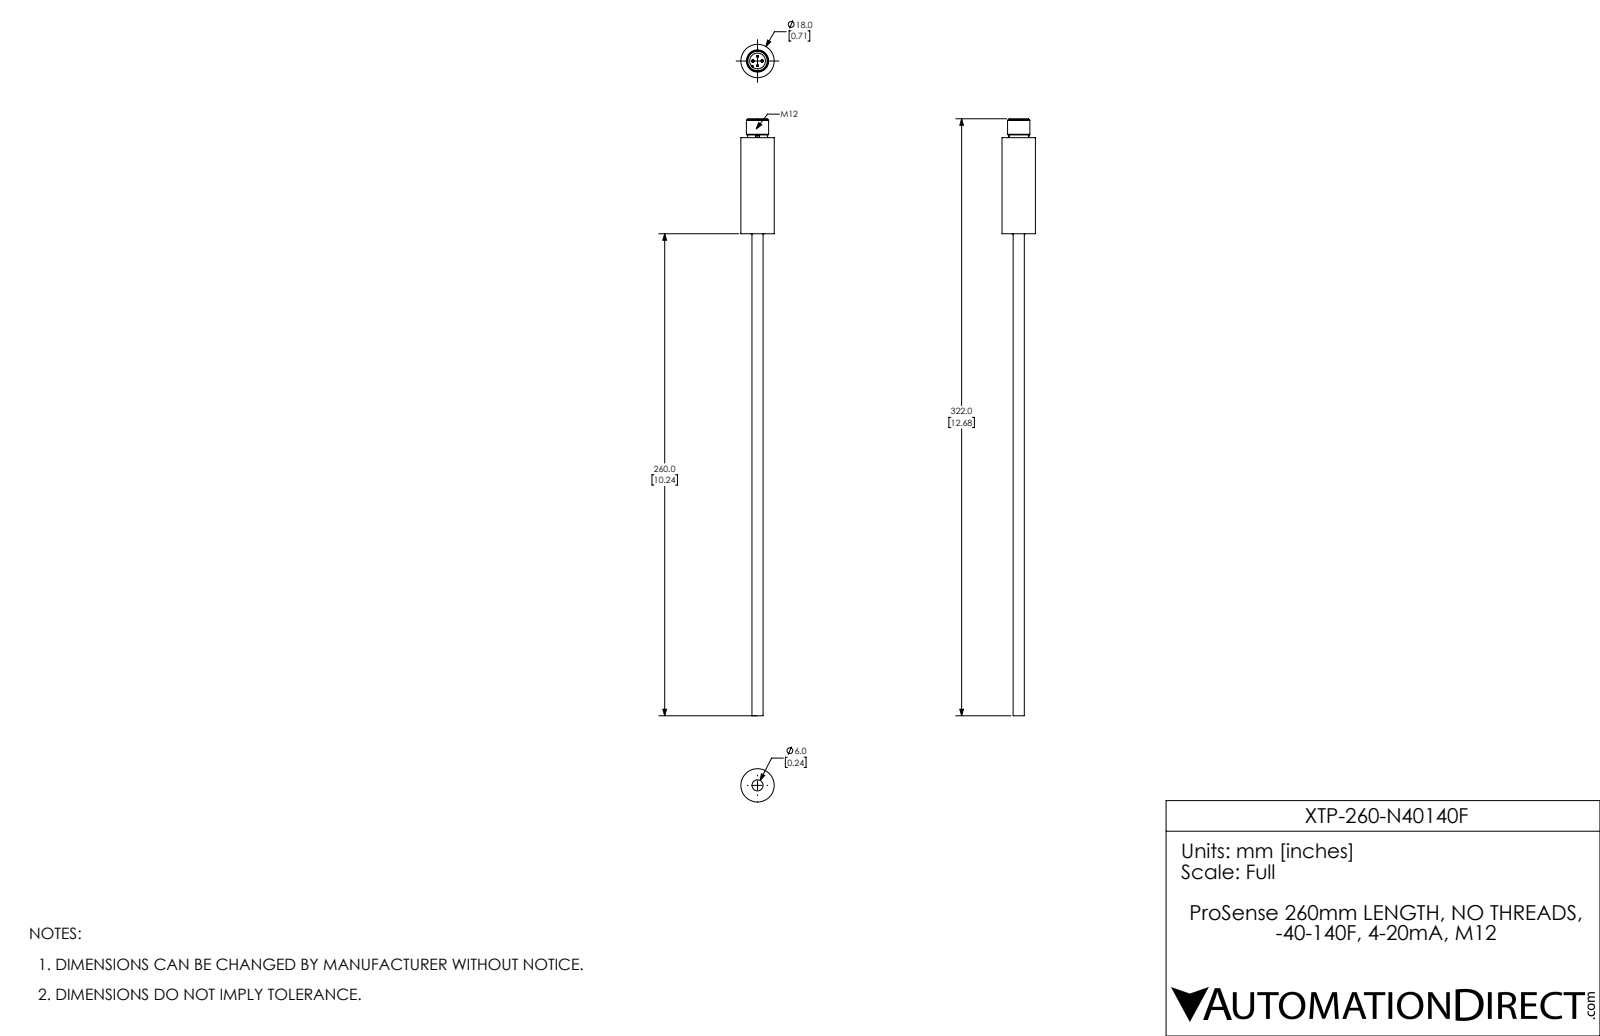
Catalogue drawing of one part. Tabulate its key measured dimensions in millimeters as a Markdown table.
| quantity | value |
| --- | --- |
| part name | XTP-260-N40140F |
| STEP written by | SolidWorks 2017 (AUTOMOTIVE_DESIGN) |
| units | millimeters |
| bodies | 1 solid, 67 faces (24 planar, 21 cylindrical, 22 other) |
| overall size | 322 × 18 × 18 |
| volume | 21 140 mm³ |
| surface area | 9 039 mm² |
| round holes (diameter × count) | 8.5 × 1 |
| round bosses / shafts (diameter × count) | 1 × 4, 18 × 1, 12 × 1, 10.7 × 1, 10.5 × 1, 6 × 1 |
| partial cylindrical surfaces (radius × count) | 0.4 × 1 |
| main face-to-face distances | 51.8, 53, 1.2, 62, 10.2, 9, 260, 311.8, 313, 322 |
